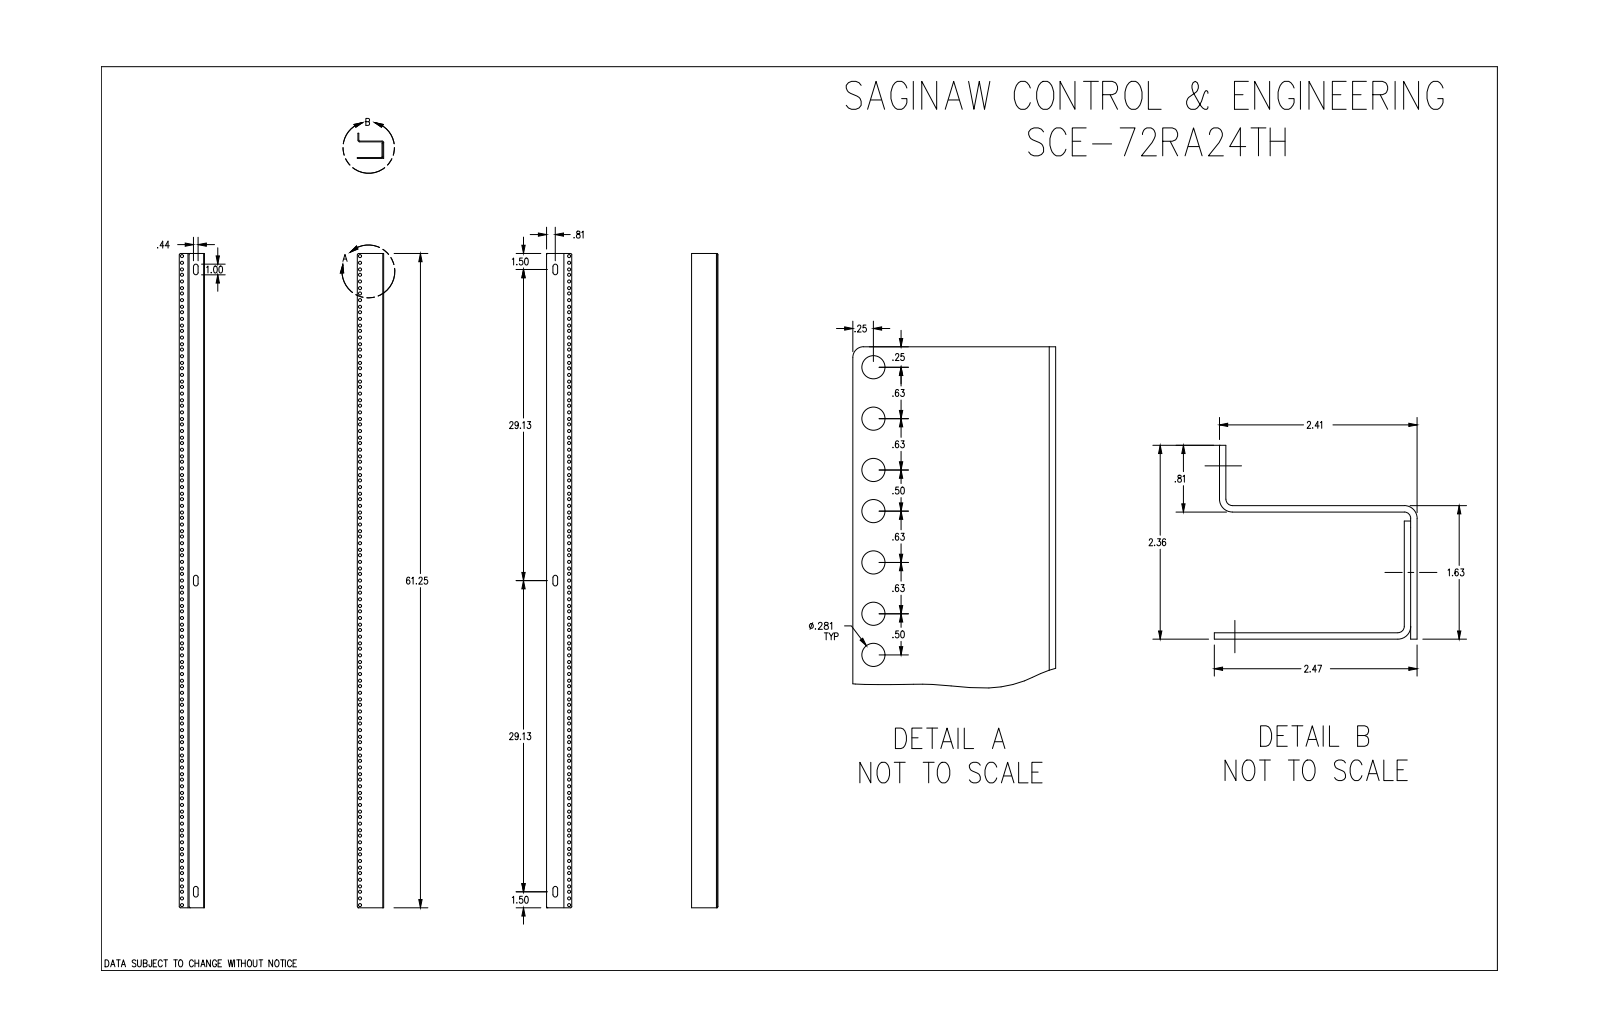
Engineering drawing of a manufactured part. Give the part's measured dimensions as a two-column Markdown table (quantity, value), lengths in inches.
| quantity | value |
| --- | --- |
| part name | SCE-72RA24TH |
| STEP written by | SolidWorks 2019 (CONFIG_CONTROL_DESIGN) |
| units | inches |
| bodies | 2 solids, 266 faces (30 planar, 236 cylindrical, 0 other) |
| overall size | 61.25 × 2.469 × 2.359 |
| volume | 38.39 in³ |
| surface area | 1 020 in² |
| round holes (diameter × count) | 0.281 × 210 |
| partial cylindrical surfaces (radius × count) | 0.219 × 6, 0.125 × 5, 0.078 × 3, 0.13 × 3, 0.156 × 3 |
| main face-to-face distances | 0.078, 1.547, 1.625, 1.469, 0.156, 2.328, 2.25, 2.406, 2.172, 1.437 |
| hole center spacings | 1.75, 3.5, 5.25, 7, 8.75, 0.625, 0.625, 1.25 |
